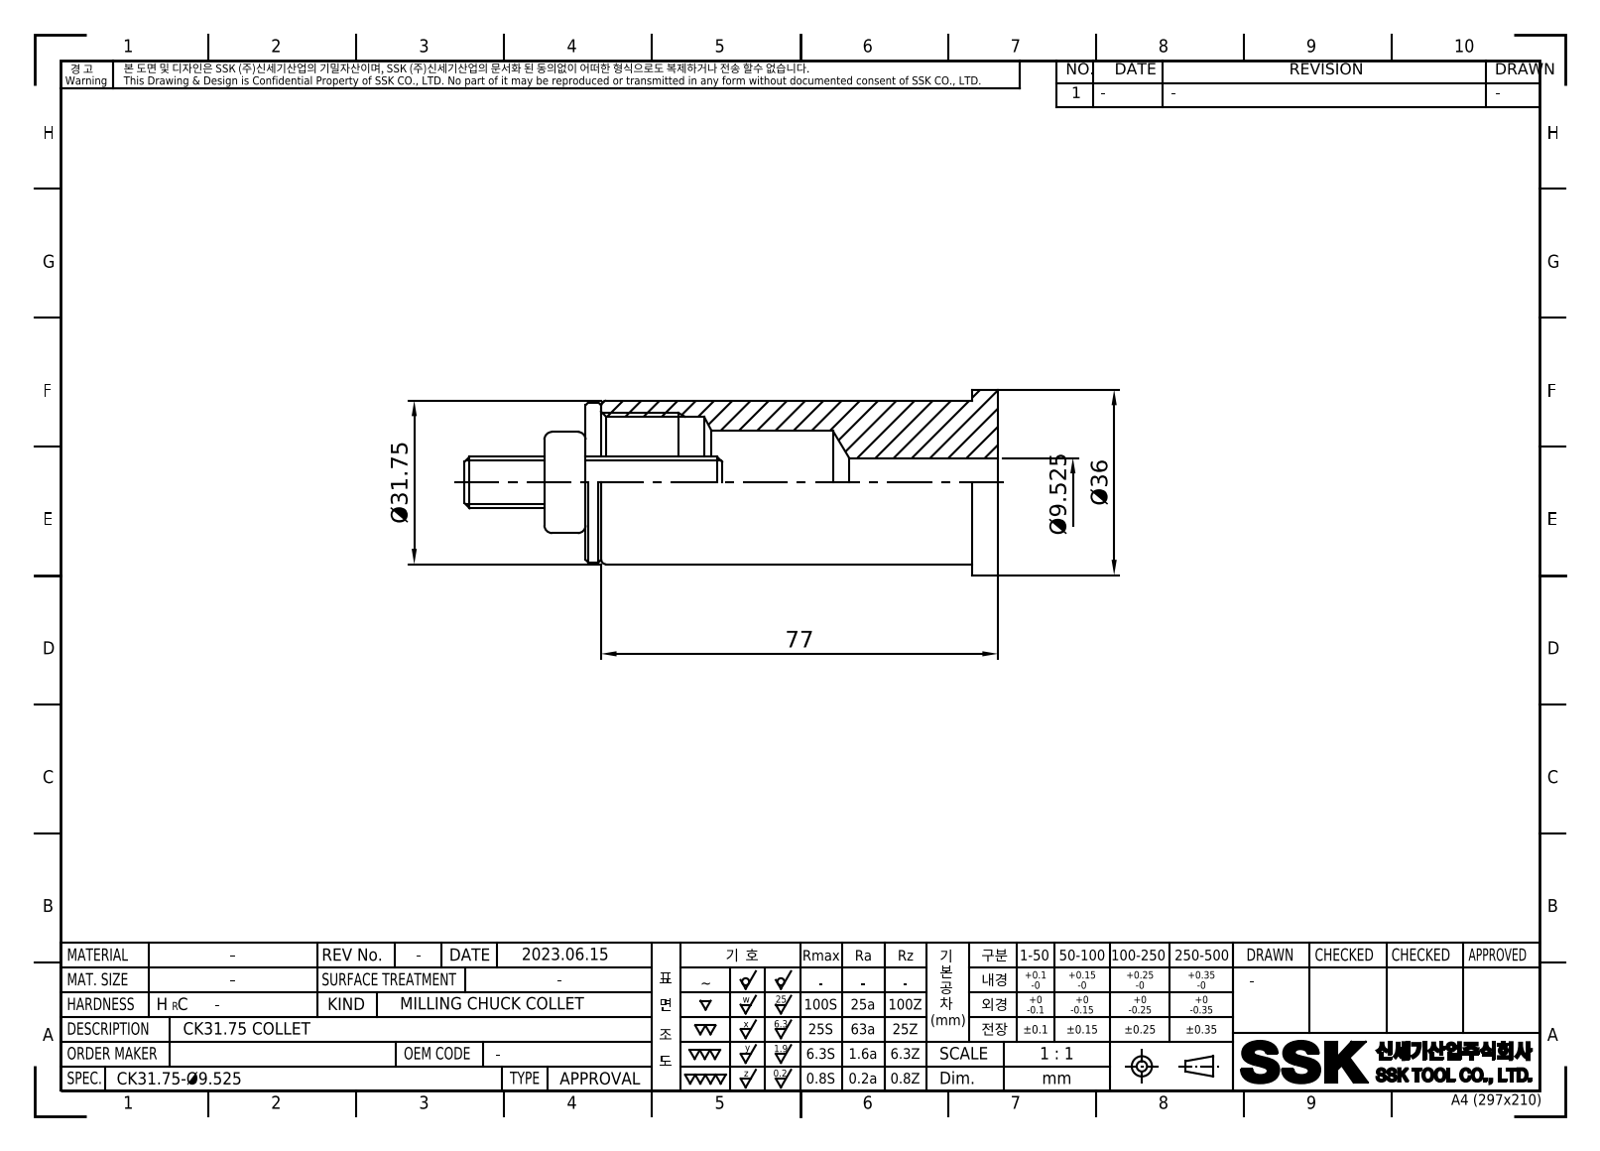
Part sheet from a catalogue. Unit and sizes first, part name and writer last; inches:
Units: inches
Overall size (bounding box): 3.031 × 1.417 × 1.417
Round holes (diameter × count): ⌀0.375 ×1, ⌀0.787 ×1, ⌀0.999 ×1
Round bosses / shafts (diameter × count): ⌀1.417 ×1, ⌀1.25 ×1
Main face-to-face distances: 3.031, 2.835, 0.197
Volume: 2.524 in³ · Surface area: 21.14 in²
Bodies: 1 solid, 10 faces (3 planar, 5 cylindrical, 2 other)
Part name (STEP PRODUCT): LO-CK31.75-9.525
STEP written by: Autodesk Inventor 2022 (AUTOMOTIVE_DESIGN)
